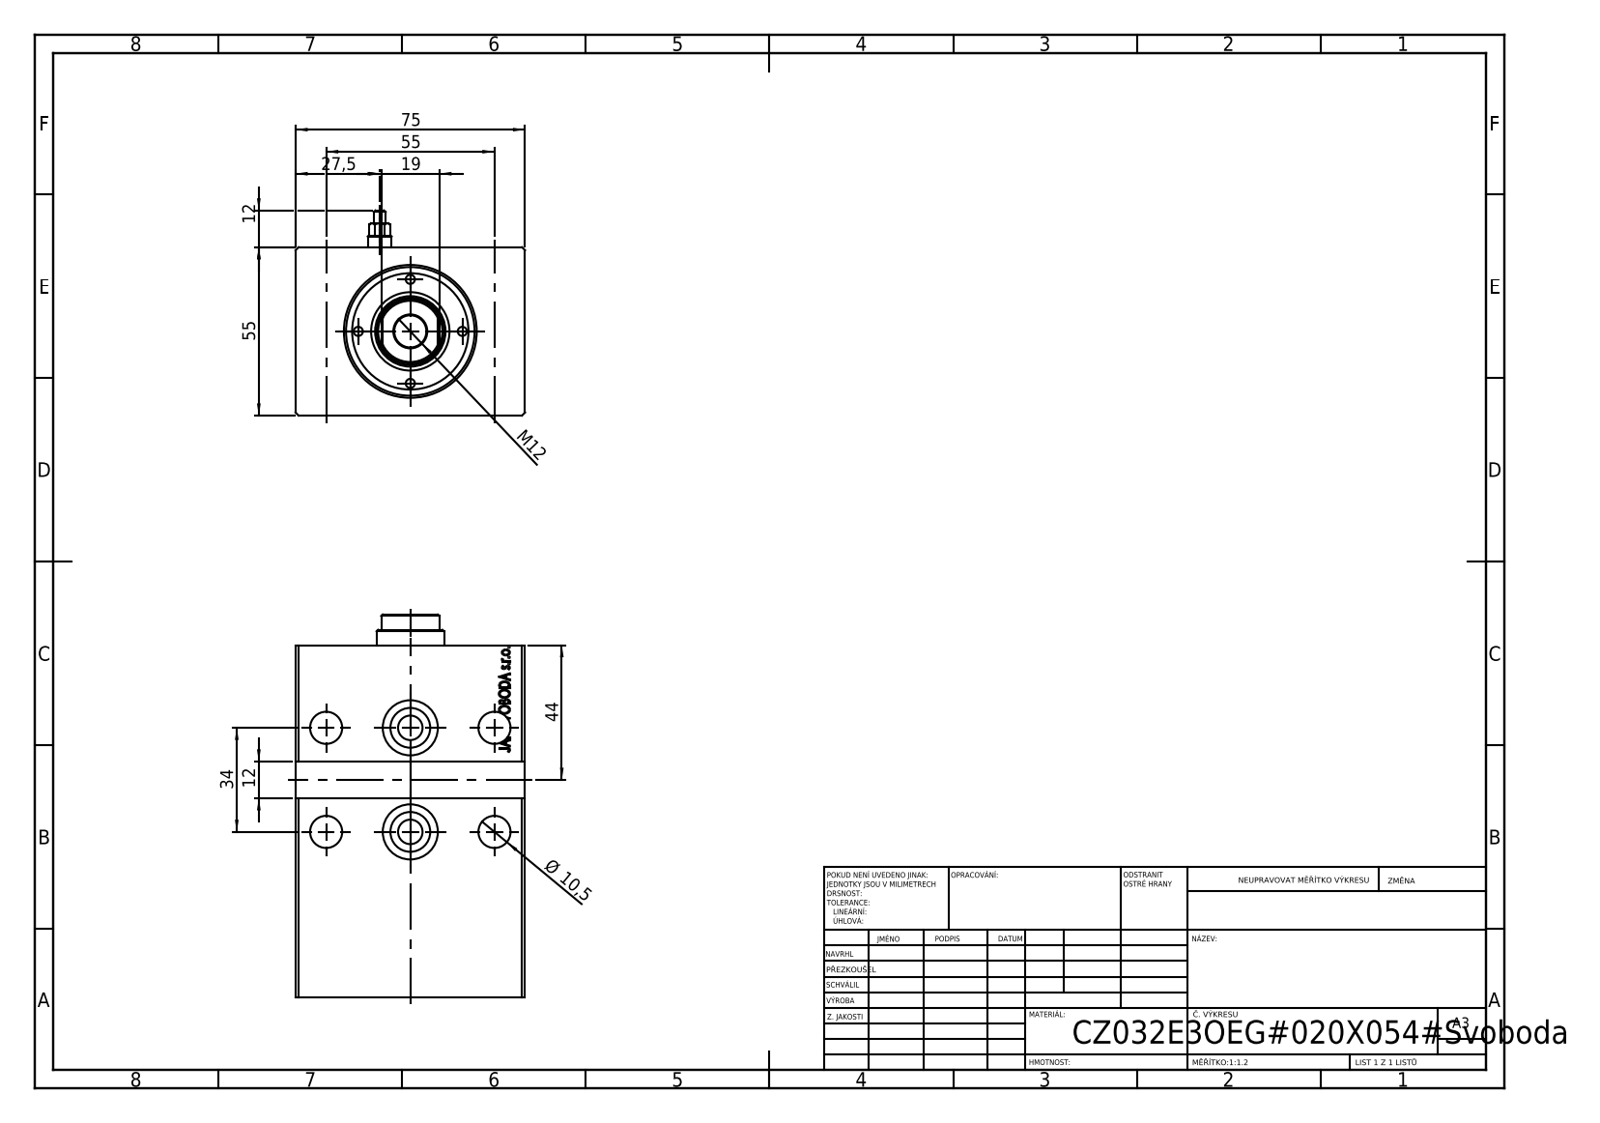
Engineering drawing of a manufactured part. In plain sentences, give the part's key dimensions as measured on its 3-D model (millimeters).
The part is named "Zatka_Cushioning3; V500CZ_VCP_E; V500CZ_B_VC; V500CZ_E". Its 3-D file was written by "SolidWorks 2019 (CONFIG_CONTROL_DESIGN)". It is 5 solids with 856 faces: 400 planar, 66 cylindrical and 390 other. Overall it measures 125 by 75 by 67 millimeters. Its volume is 444 677 cubic millimeters and its surface area 73 035 square millimeters. Round holes: 5 of diameter 10.5, 4 of diameter 3, 4 of diameter 8, 2 of diameter 1.8, 2 of diameter 18, 1 of diameter 22, 1 of diameter 23, 1 of diameter 32, 1 of diameter 36, 1 of diameter 42. Round bosses or shafts: 2 of diameter 13, 2 of diameter 7.8, 2 of diameter 3.8, 1 of diameter 38. Partial cylindrical surfaces (rounded edges, fillets, slot ends): 1 of radius 10.5. The main face-to-face distances are 55, 75, 115, 10, 101.2, 13.8, 91.2, 105, 114.8, 104.8. The hole center spacings are 34, 17, 24.04, 27.5, 43.73, 55, 64.66, 11.66.
